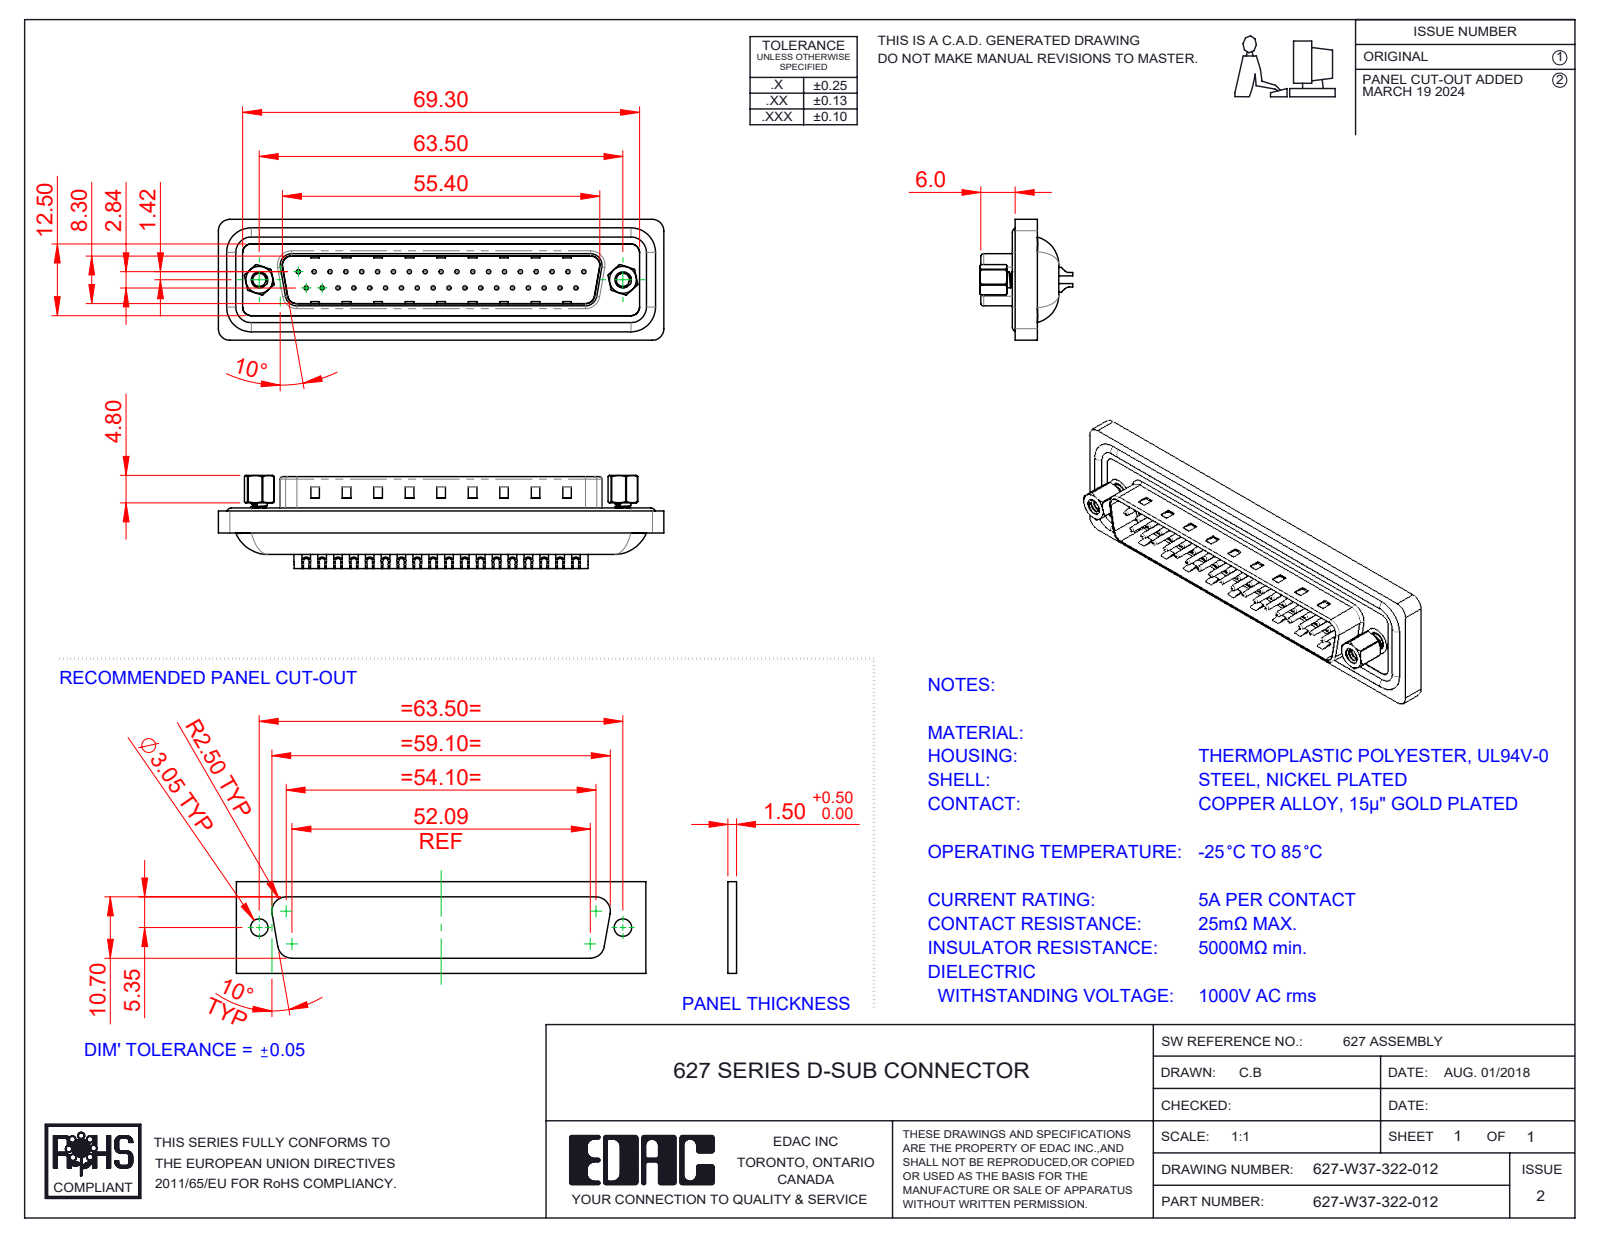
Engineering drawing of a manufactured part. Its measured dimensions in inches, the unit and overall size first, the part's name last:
Units: inches
Overall size (bounding box): 3.063 × 0.831 × 0.64
Round holes (diameter × count): ⌀0.03 ×37, ⌀0.039 ×37, ⌀0.059 ×37, ⌀0.063 ×37, ⌀0.079 ×37, ⌀0.089 ×2, ⌀0.09 ×2, ⌀0.157 ×2, ⌀0.189 ×2, ⌀0.197 ×2
Round bosses / shafts (diameter × count): ⌀0.059 ×9, ⌀0.063 ×4, ⌀0.193 ×2, ⌀0.11 ×2
Partial cylindrical surfaces — rounded edges, fillets, slot ends (radius × count): R0.079 ×16, R0.059 ×14, R0.02 ×8, R0.106 ×6, R0.035 ×4, R0.063 ×4, R0.169 ×4, R0.016 ×2
Main face-to-face distances: 0.03, 0.016, 0.161, 0.043, 0.108, 0.181, 0.148, 0.222, 0.608, 0.579
Hole centre spacings: 0.124, 0.109, 0.218, 0.327, 0.198, 0.398, 0.436, 0.503
Volume: 0.584 in³ · Surface area: 22.66 in²
Bodies: 45 solids, 1999 faces (570 planar, 890 cylindrical, 539 other)
Part name (STEP PRODUCT): 627W 4-40 Threaded Rivet; 627W Housing_37 Contacts; 627W Waterproof Housing_37 Contacts; 627W Contact Row 2_22 (+4 more)
STEP written by: SolidWorks 2023 (CONFIG_CONTROL_DESIGN)
